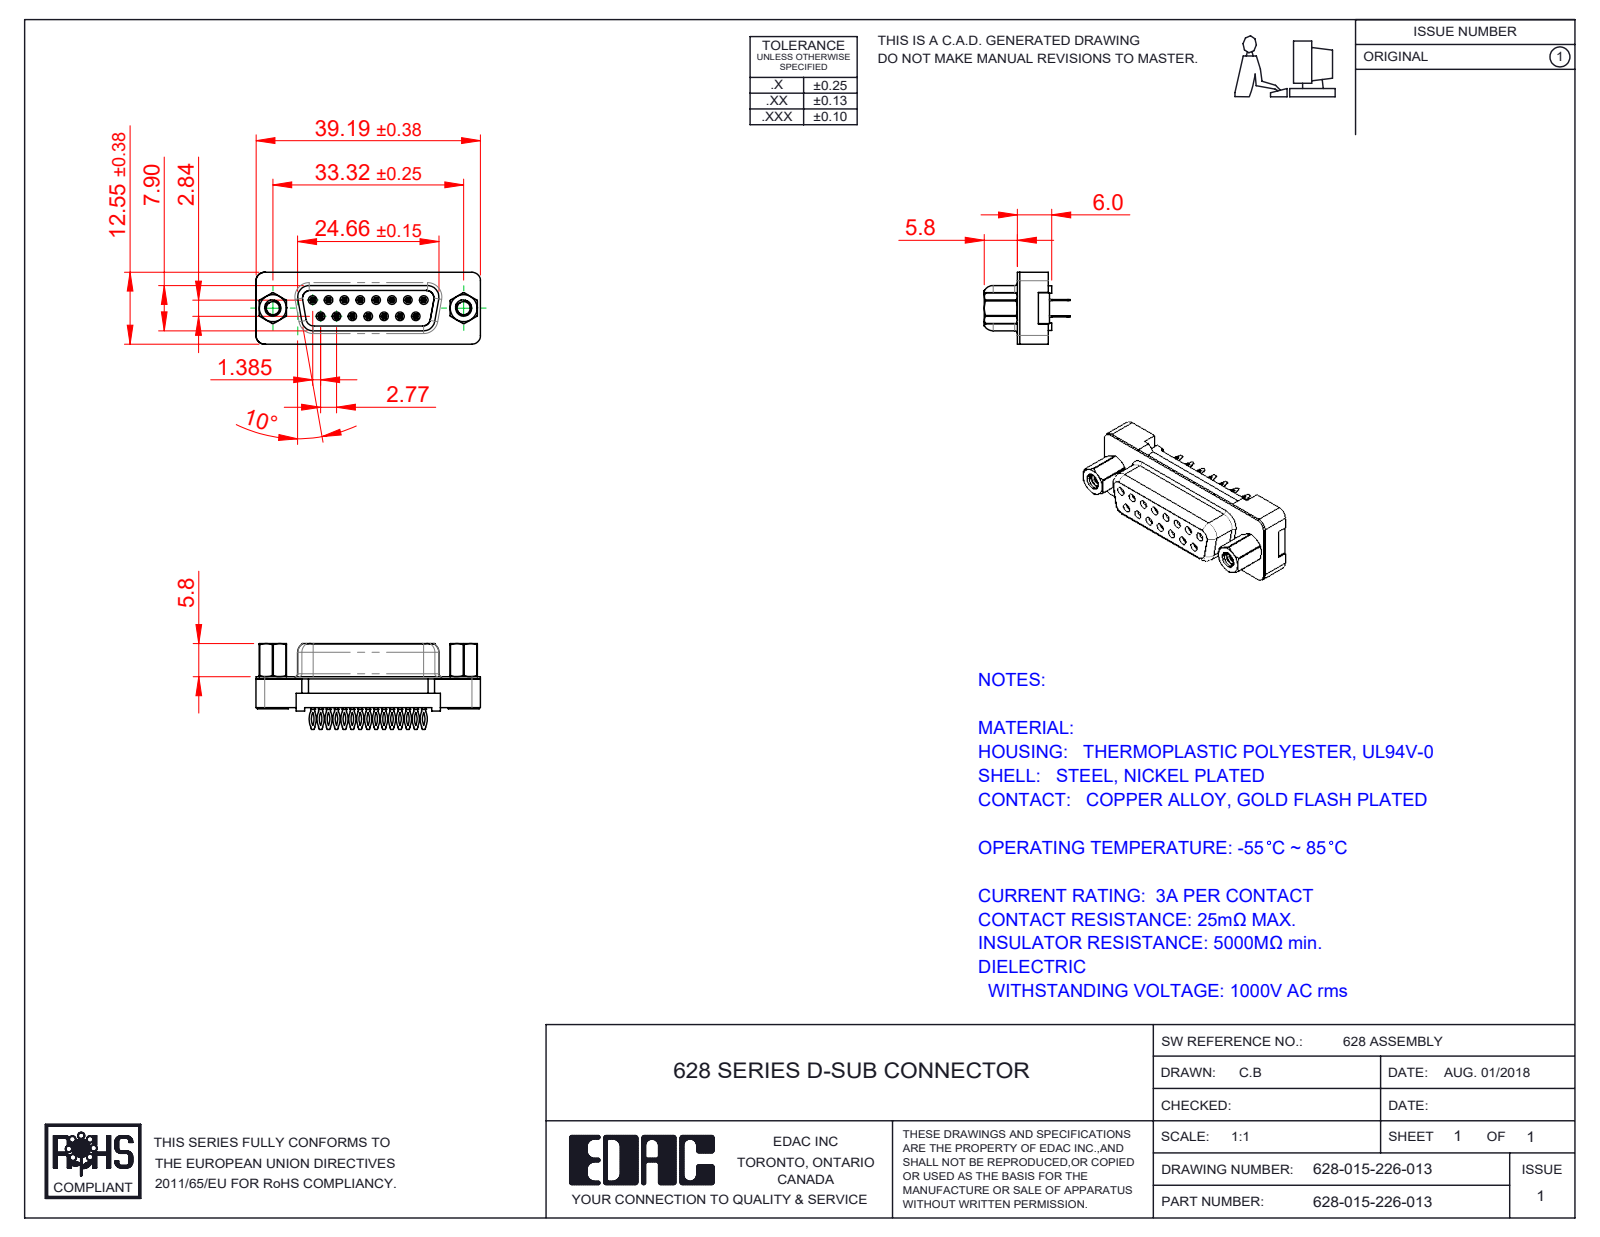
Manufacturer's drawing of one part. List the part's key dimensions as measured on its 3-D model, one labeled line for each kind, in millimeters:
Part name (STEP PRODUCT): 628 PB Contact Row 1_26; 628 Plastic Body Housing_15 Contacts; 628-015-226-013; 628 PB Contact Row 2_26 (+3 more)
STEP written by: SolidWorks 2020 (CONFIG_CONTROL_DESIGN)
Units: millimetres
Bodies: 21 solids, 1721 faces (676 planar, 476 cylindrical, 569 other)
Overall size (bounding box): 39.2 × 15 × 12.55
Volume: 2 664 mm³ · Surface area: 6 386 mm²
Round holes (diameter × count): ⌀0.9 ×15, ⌀2.26 ×2, ⌀2.29 ×2, ⌀3.05 ×2, ⌀4 ×2, ⌀4.8 ×2, ⌀5 ×2
Round bosses / shafts (diameter × count): ⌀4.9 ×2, ⌀2.79 ×2
Partial cylindrical surfaces — rounded edges, fillets, slot ends (radius × count): R0.25 ×60, R2.92 ×30, R3.33 ×30, R0.5 ×19, R0.3 ×15, R1.35 ×12, R1.5 ×8, R0.9 ×4
Main face-to-face distances: 0.4, 5.54, 2, 2.5, 6.2, 2.77, 0.68, 5.52, 2.68, 3.52
Hole centre spacings: 3.16, 2.77, 5.54, 8.31, 11.08, 5.03, 5.04, 7.48
